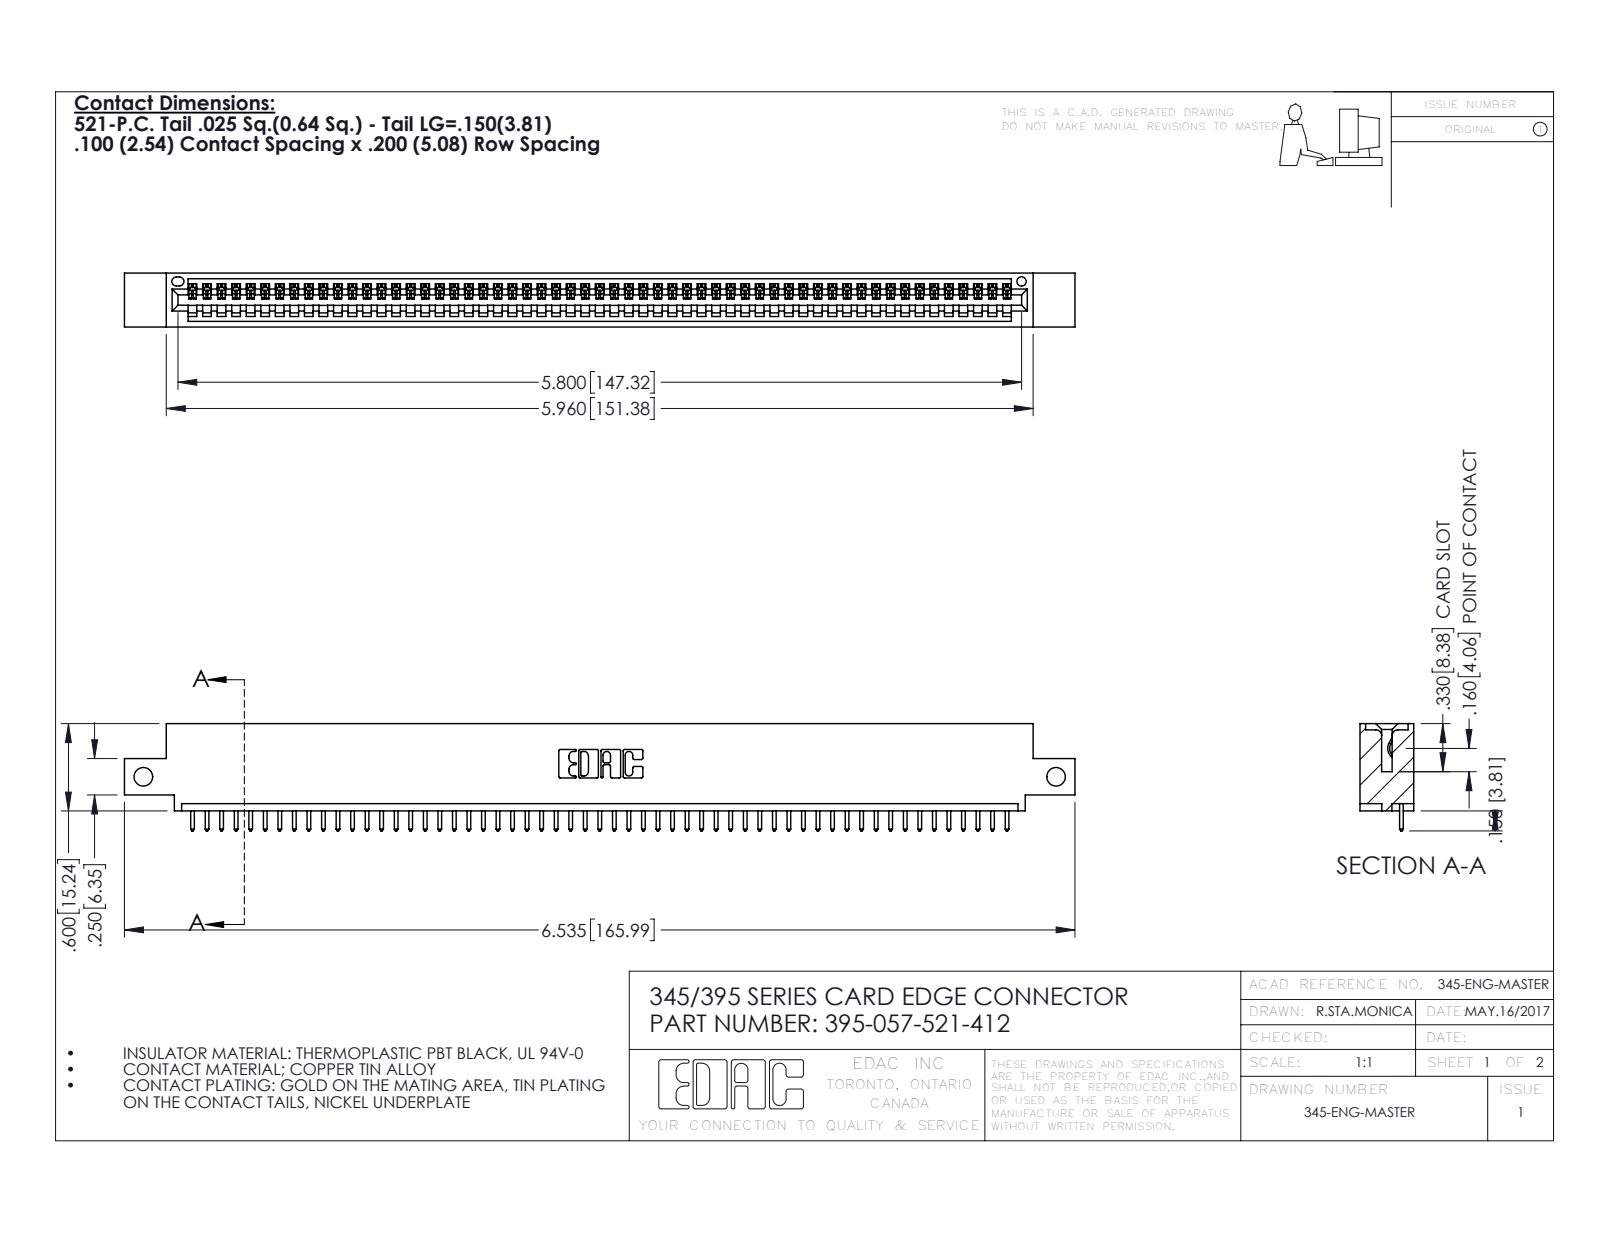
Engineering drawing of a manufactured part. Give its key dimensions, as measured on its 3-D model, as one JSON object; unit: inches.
{"part_name": "345-292-001_345-293-121; 395-057-521-412; 345 Part_0.110 Offset - Side Mount", "step_written_by": "SolidWorks 2016 (CONFIG_CONTROL_DESIGN)", "units": "inches", "bodies": {"solids": 58, "faces": 3436, "planar": 2364, "cylindrical": 1072, "other": 0}, "overall_size": [6.535, 0.737, 0.37], "volume_in3": 0.95, "surface_area_in2": 31.3, "round_holes": [[0.128, 2], [0.064, 1]], "partial_cylinders_radius": [[0.006, 114], [0.01, 114], [0.01, 22], [0.007, 6], [0.031, 6], [0.026, 3], [0.031, 2], [0.04, 2]], "face_to_face_distances": [0.298, 0.072, 0.37, 0.2, 0.098, 0.272, 0.025, 0.225, 0.149, 0.072], "hole_center_spacings": [6.275]}
